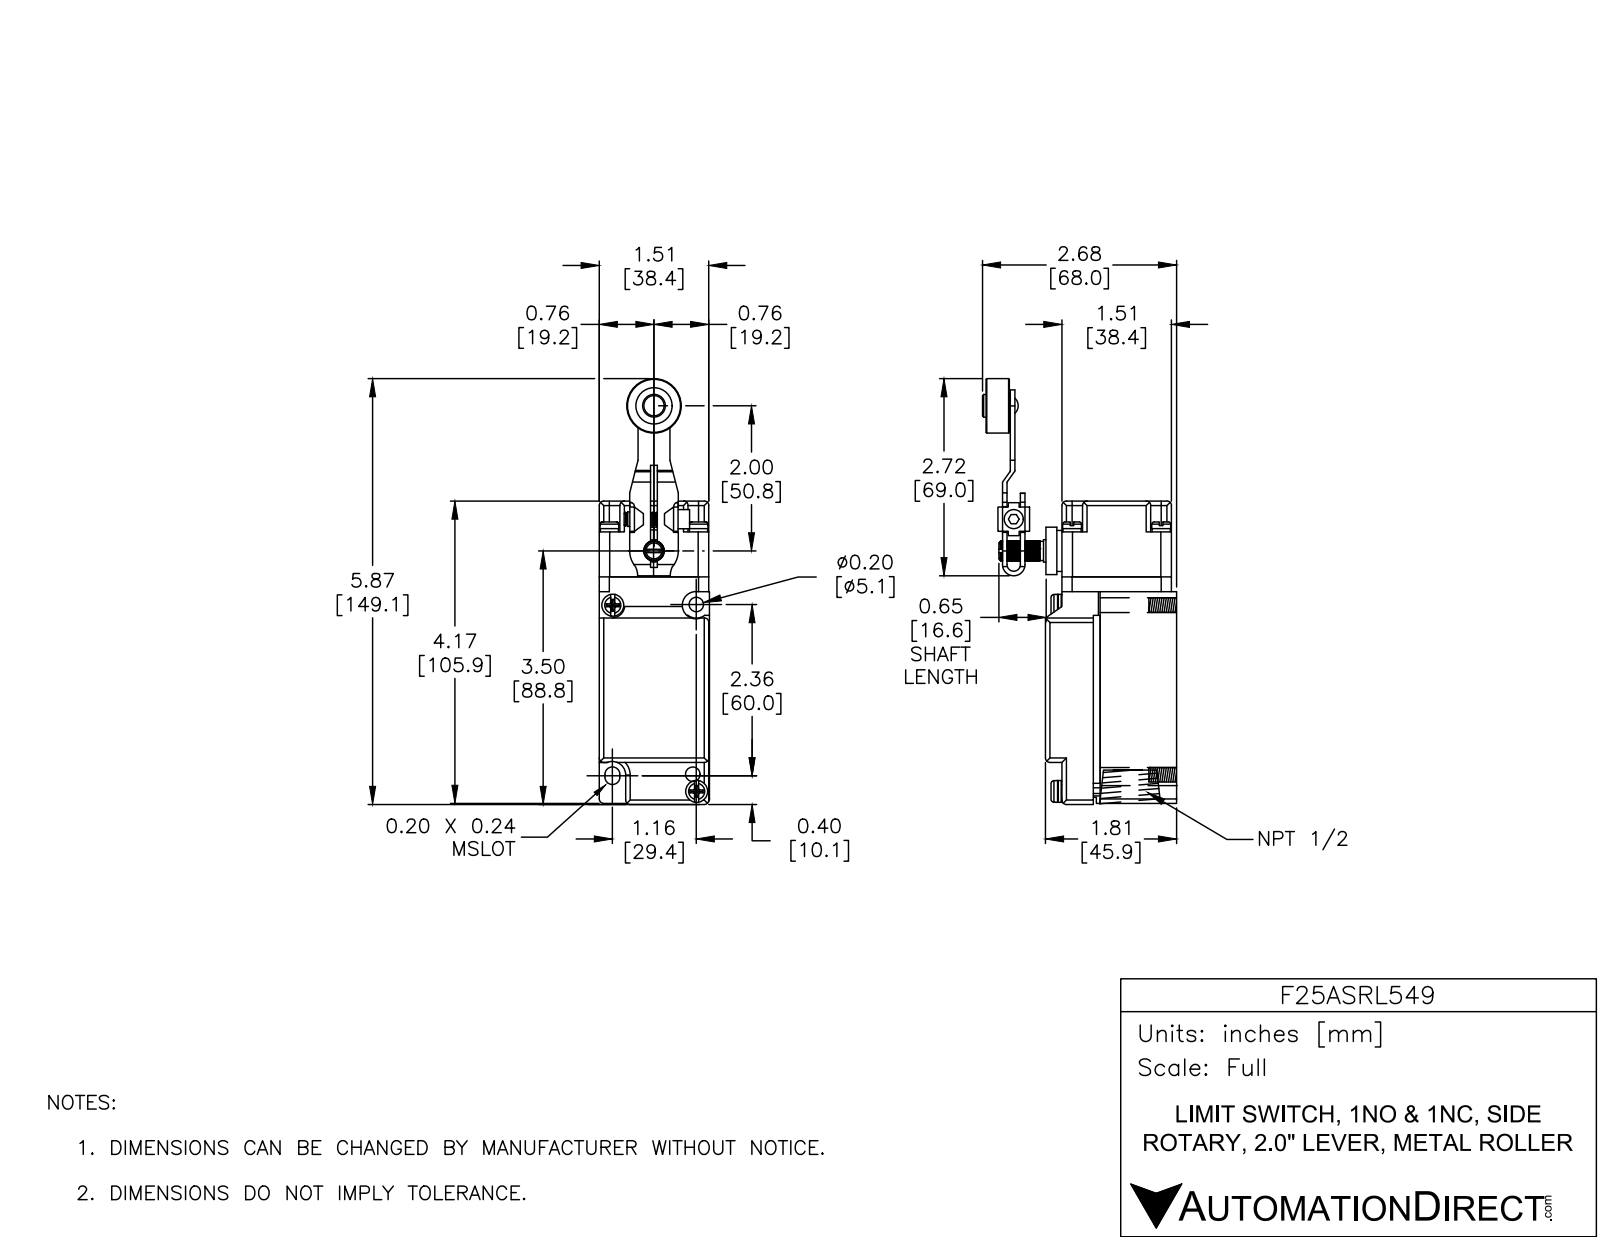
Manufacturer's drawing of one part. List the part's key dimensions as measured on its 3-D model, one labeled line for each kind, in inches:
Part name (STEP PRODUCT): Imported181; Imported167; Imported170; Imported169 (+8 more)
STEP written by: SolidWorks 2002296 (CONFIG_CONTROL_DESIGN)
Units: inches
Bodies: 17 solids, 927 faces (512 planar, 233 cylindrical, 182 other)
Overall size (bounding box): 5.872 × 2.678 × 1.52
Volume: 10.37 in³ · Surface area: 74.26 in²
Round holes (diameter × count): ⌀0.177 ×4, ⌀0.19 ×3, ⌀0.2 ×3, ⌀0.156 ×1, ⌀0.17 ×1, ⌀0.25 ×1, ⌀0.5 ×1, ⌀0.58 ×1
Round bosses / shafts (diameter × count): ⌀0.26 ×4, ⌀0.25 ×4, ⌀0.302 ×2, ⌀0.3 ×2, ⌀0.75 ×1, ⌀0.655 ×1, ⌀0.565 ×1, ⌀0.375 ×1
Partial cylindrical surfaces — rounded edges, fillets, slot ends (radius × count): R0.062 ×29, R0.03 ×16, R0.015 ×8, R0.145 ×8, R0.063 ×4, R0.14 ×4, R0.032 ×3, R0.025 ×2
Main face-to-face distances: 0.094, 1.149, 1.055, 1.52, 0.66, 0.754, 1.809, 1.51, 0.227, 0.433
Hole centre spacings: 1.23, 1.23, 1.74, 2.815, 0.225, 0.235, 0.936, 0.942
